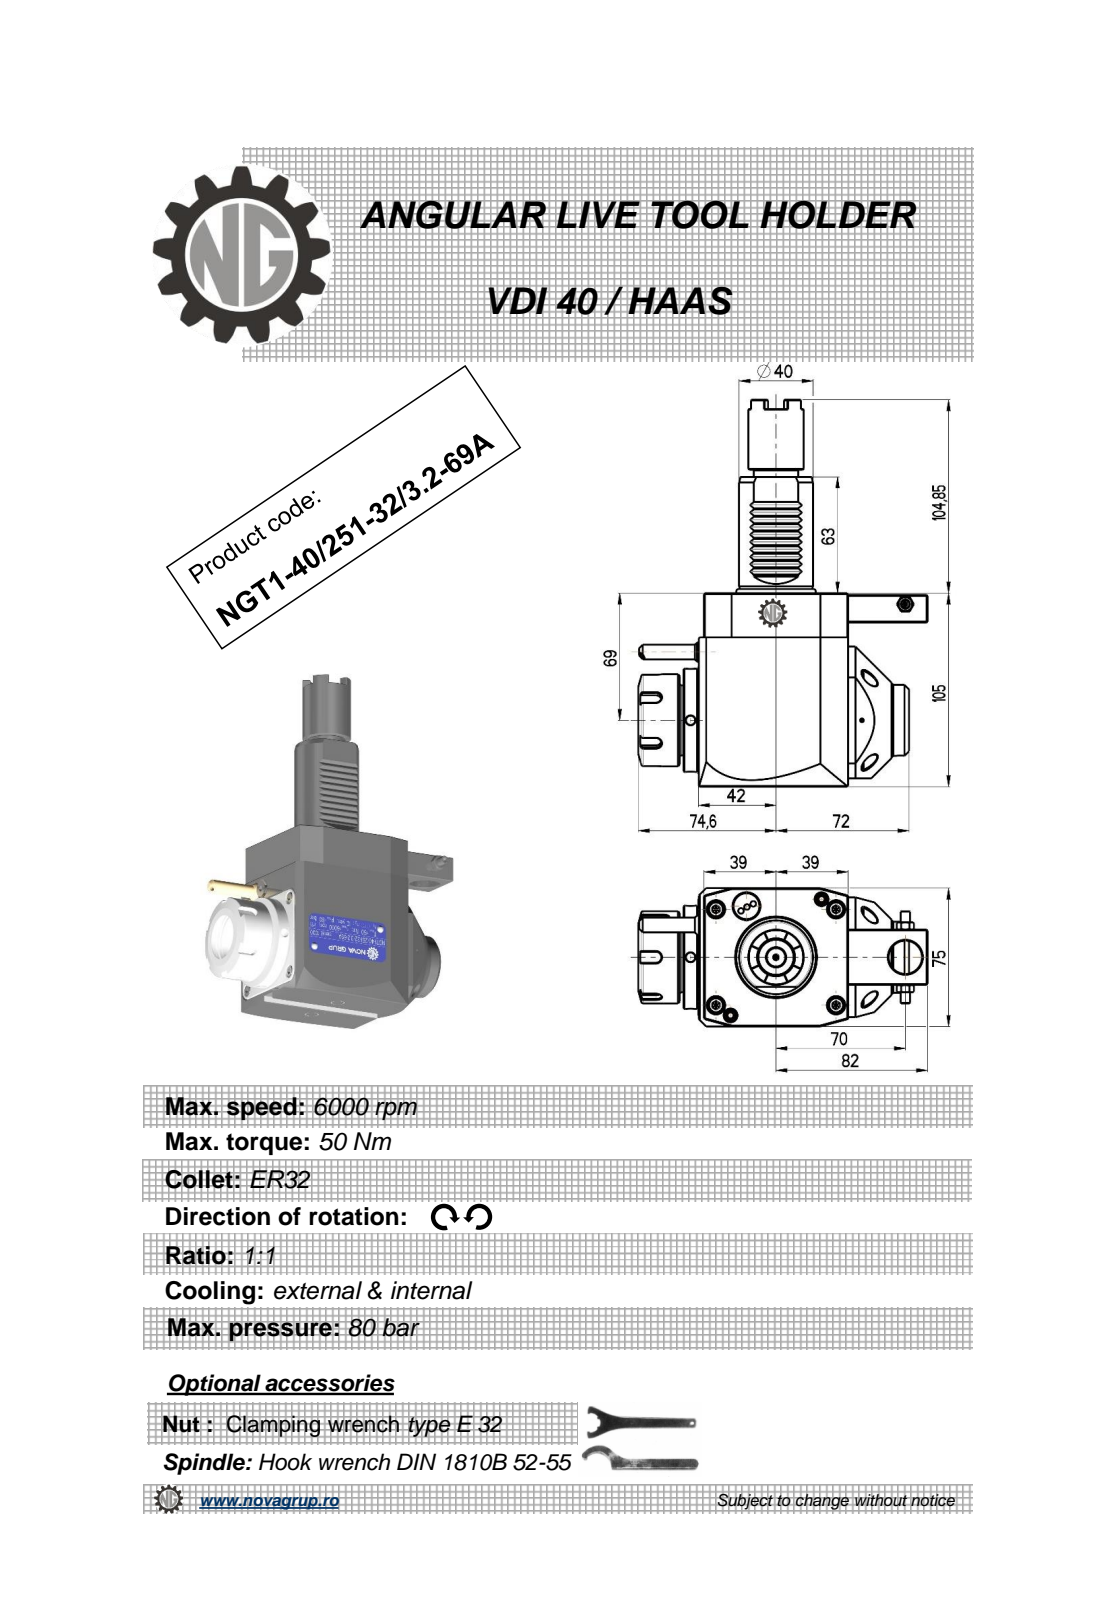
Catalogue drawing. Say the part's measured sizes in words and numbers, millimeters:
The part is named "NGT1_40_251_32_3_2_69A". Its 3-D file was written by "PRO/ENGINEER BY PARAMETRIC TECHNOLOGY CORPORATION, 2010280 (CONFIG_CONTROL_DESIGN)". It is 1 solid with 453 faces: 216 planar, 91 cylindrical and 146 other. Overall it measures 209.85 by 156.6 by 75 millimeters. Its volume is 879 146 cubic millimeters and its surface area 75 259 square millimeters. Round holes: 3 of diameter 5, 1 of diameter 3, 1 of diameter 4.2, 1 of diameter 9.5, 1 of diameter 18, 1 of diameter 27. Round bosses or shafts: 1 of diameter 56, 1 of diameter 50, 1 of diameter 43, 1 of diameter 40, 1 of diameter 38.5, 1 of diameter 30, 1 of diameter 24, 1 of diameter 10. Partial cylindrical surfaces (rounded edges, fillets, slot ends): 12 of radius 0.26, 10 of radius 0.3, 6 of radius 0.2, 5 of radius 3, 1 of radius 0.5, 1 of radius 10, 1 of radius 40. The main face-to-face distances are 75, 105, 81, 89, 1, 3, 2.8, 78, 80.8, 22.5. The hole center spacings are 30.11, 40.93, 61.5, 116.25, 132.22.
